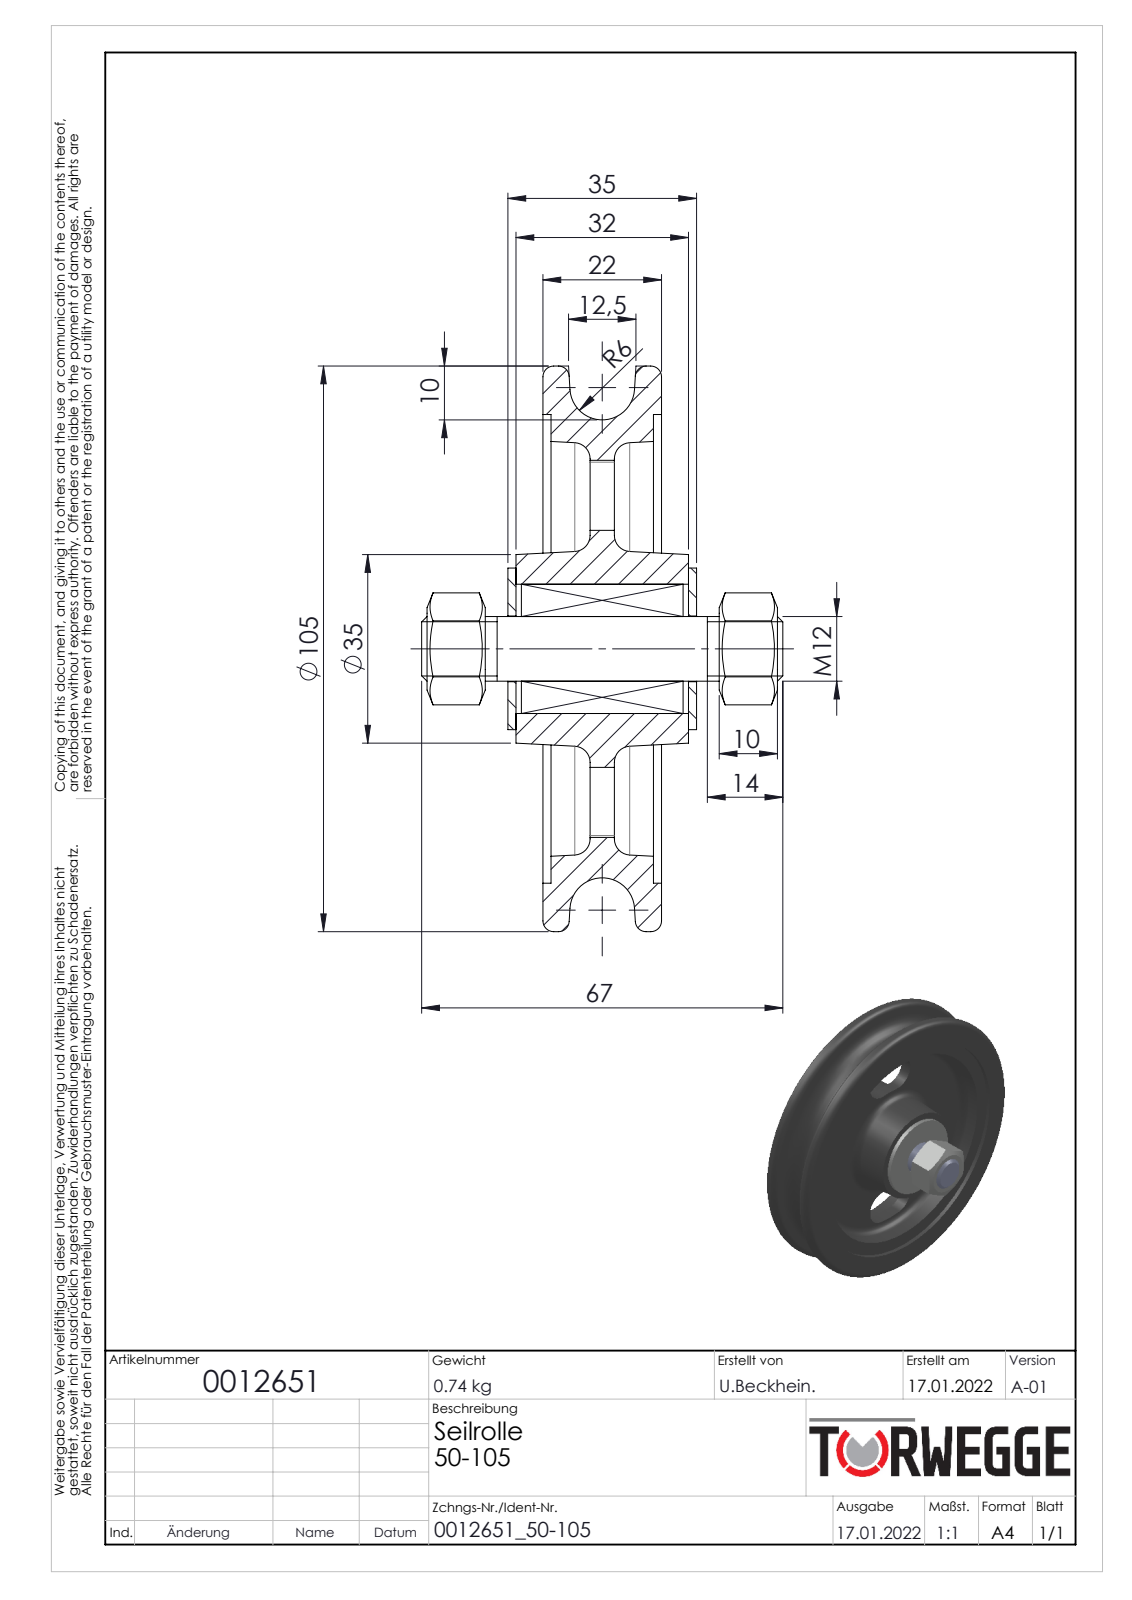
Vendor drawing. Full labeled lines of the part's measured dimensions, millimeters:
Part name (STEP PRODUCT): 0012651
STEP written by: SolidWorks 2020 (AUTOMOTIVE_DESIGN)
Units: millimetres
Bodies: 7 solids, 122 faces (32 planar, 38 cylindrical, 52 other)
Overall size (bounding box): 105 × 105 × 67
Volume: 108 630 mm³ · Surface area: 46 696 mm²
Round holes (diameter × count): ⌀10.11 ×1, ⌀12 ×1, ⌀12.2 ×1, ⌀24 ×1, ⌀87 ×1
Round bosses / shafts (diameter × count): ⌀105 ×1, ⌀30 ×1
Partial cylindrical surfaces — rounded edges, fillets, slot ends (radius × count): R6.5 ×4, R22 ×1, R35 ×1
Main face-to-face distances: 8.75, 13.25, 1.5, 6.5, 27, 20.5, 7.25, 11.75, 5, 13.75
